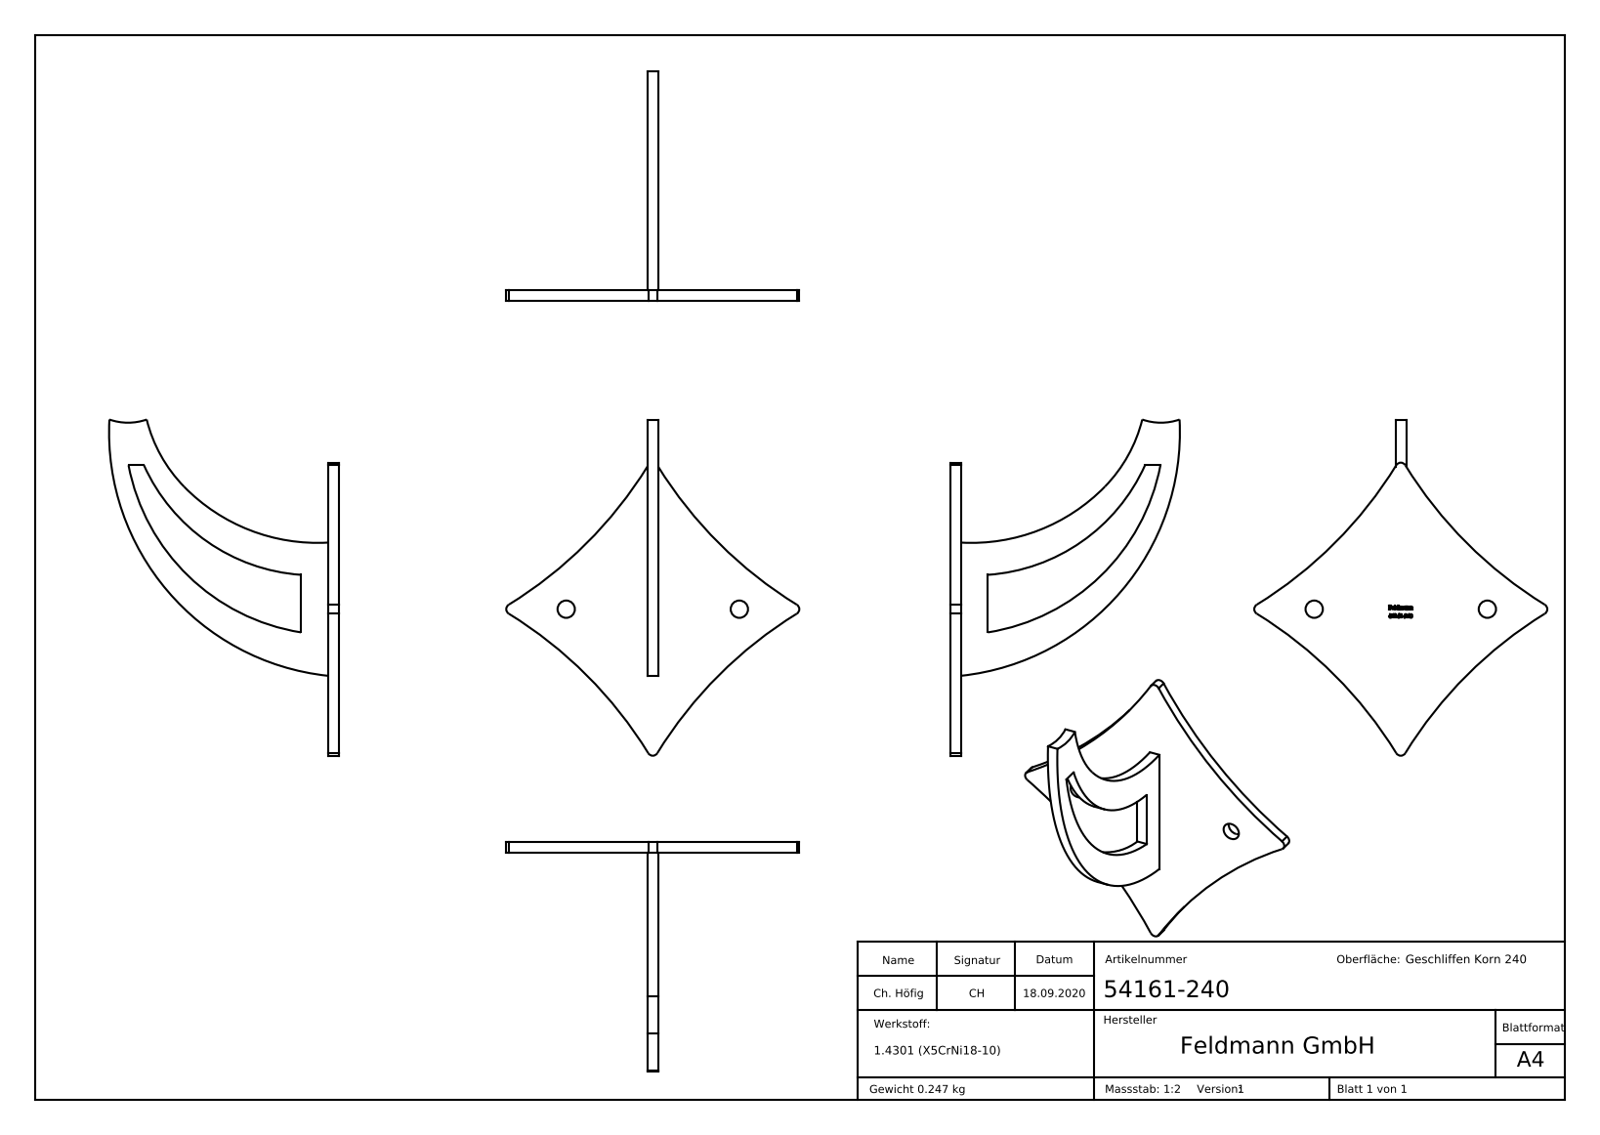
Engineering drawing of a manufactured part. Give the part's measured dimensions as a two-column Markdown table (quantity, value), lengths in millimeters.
| quantity | value |
| --- | --- |
| part name | 54161-240 |
| STEP written by | SolidWorks 2018 (CONFIG_CONTROL_DESIGN) |
| units | millimeters |
| bodies | 1 solid, 240 faces (141 planar, 19 cylindrical, 80 other) |
| overall size | 126.19 × 110 × 86.12 |
| volume | 31 256 mm³ |
| surface area | 18 627 mm² |
| round holes (diameter × count) | 6.5 × 2 |
| partial cylindrical surfaces (radius × count) | 2 × 4, 160 × 4, 70 × 2, 21.2 × 1, 55 × 1, 78.5 × 1, 92 × 1 |
| main face-to-face distances | 4, 14.1, 10.1, 3.9, 14, 1.14, 3.2, 0.39, 0.68, 2.03 |
| hole center spacings | 65 |
